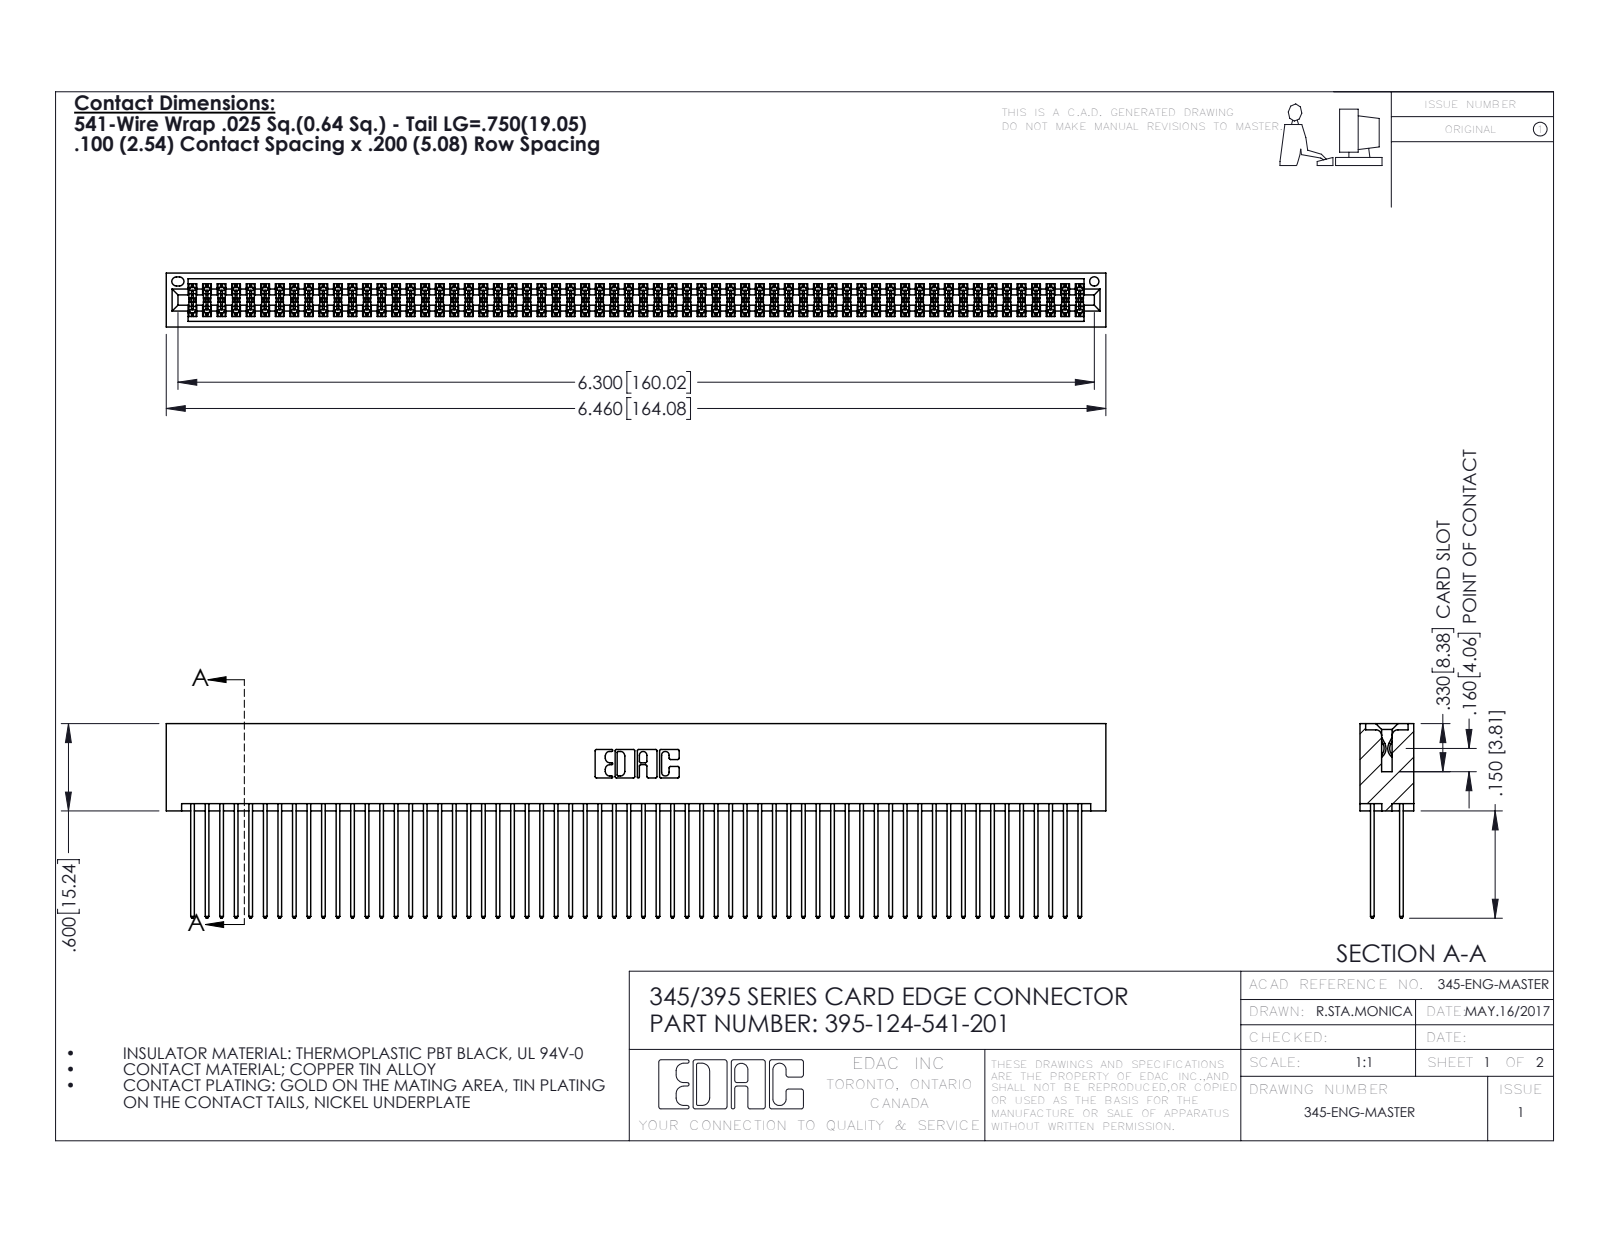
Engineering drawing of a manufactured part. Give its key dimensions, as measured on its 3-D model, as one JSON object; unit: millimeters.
{"part_name": "345 Part_No Mounting Lugs; 395-124-541-201; 345-292-001_345-293-141", "step_written_by": "SolidWorks 2016 (CONFIG_CONTROL_DESIGN)", "units": "millimeters", "bodies": {"solids": 125, "faces": 6318, "planar": 4168, "cylindrical": 2150, "other": 0}, "overall_size": [164.1, 34, 9.4], "volume_mm3": 17450, "surface_area_mm2": 29830, "round_holes": [[1.6, 1]], "partial_cylinders_radius": [[0.2, 186], [0.3, 124], [0.3, 22], [0.2, 6], [0.8, 6], [0.7, 3], [0.4, 2], [0.5, 2]], "face_to_face_distances": [7.6, 1.8, 5.1, 2.5, 6.9, 0.6, 5.7, 9.4, 4.4, 3.8]}
